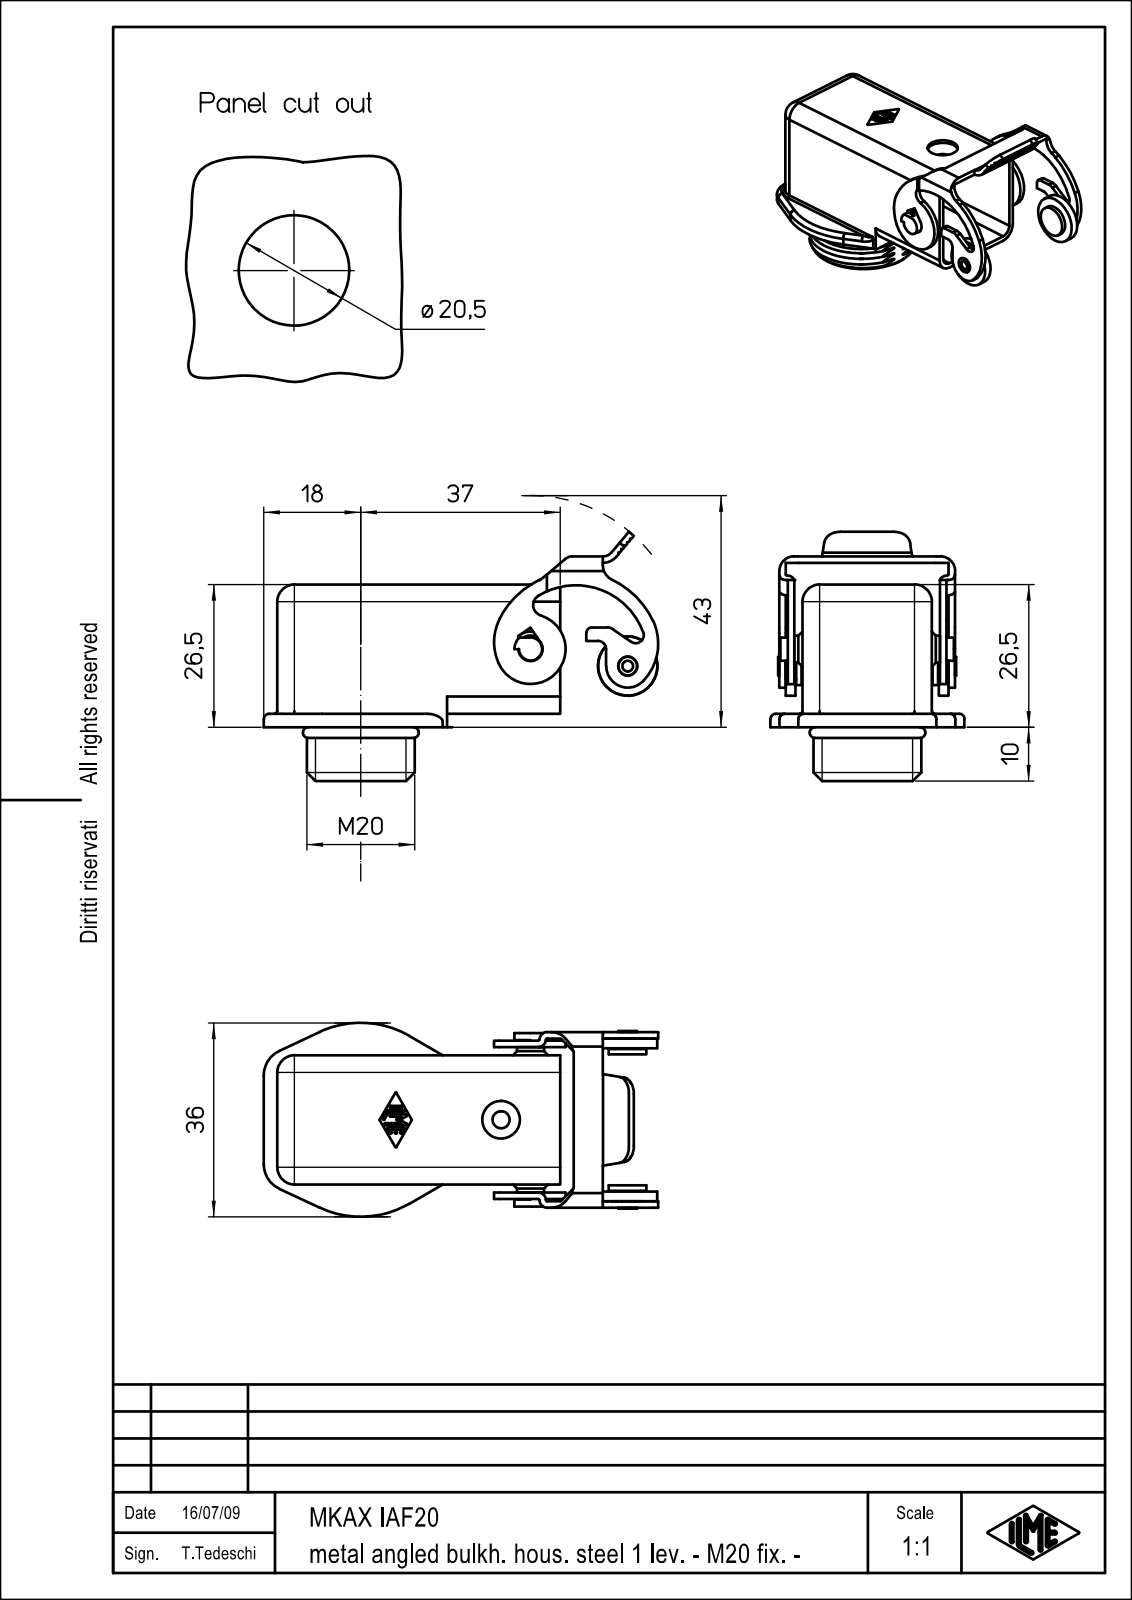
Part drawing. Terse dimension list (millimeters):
name: CUSTODIA; LEVA; MKAX_IAF20
written by: CoCreate Modeling 16.00A 16-Aug-2008 (C) Parametric Technology GmbH (AUTOMOTIVE_DESIGN)
unit: mm
bodies: 1 solid, 342 faces (146 planar, 165 cylindrical, 31 other)
size: 73.16 × 46.3 × 36
volume: 11 238 mm³; area: 14 985 mm²
holes: 1× ⌀2, 1× ⌀3.2, 1× ⌀5, 1× ⌀7, 1× ⌀14
bosses: 1× ⌀17.8, 1× ⌀11, 1× ⌀7, 1× ⌀5, 1× ⌀4.8, 1× ⌀4.3, 1× ⌀3.5
rounds: 15× R0.2, 12× R2, 8× R3.2, 6× R1, 5× R3, 4× R1.4, 3× R0.1, 3× R0.5
face distances: 24, 26.5, 1.2, 1.5, 29.8, 1.6, 2.5, 28, 4.3, 28.3
hole spacings: 26
